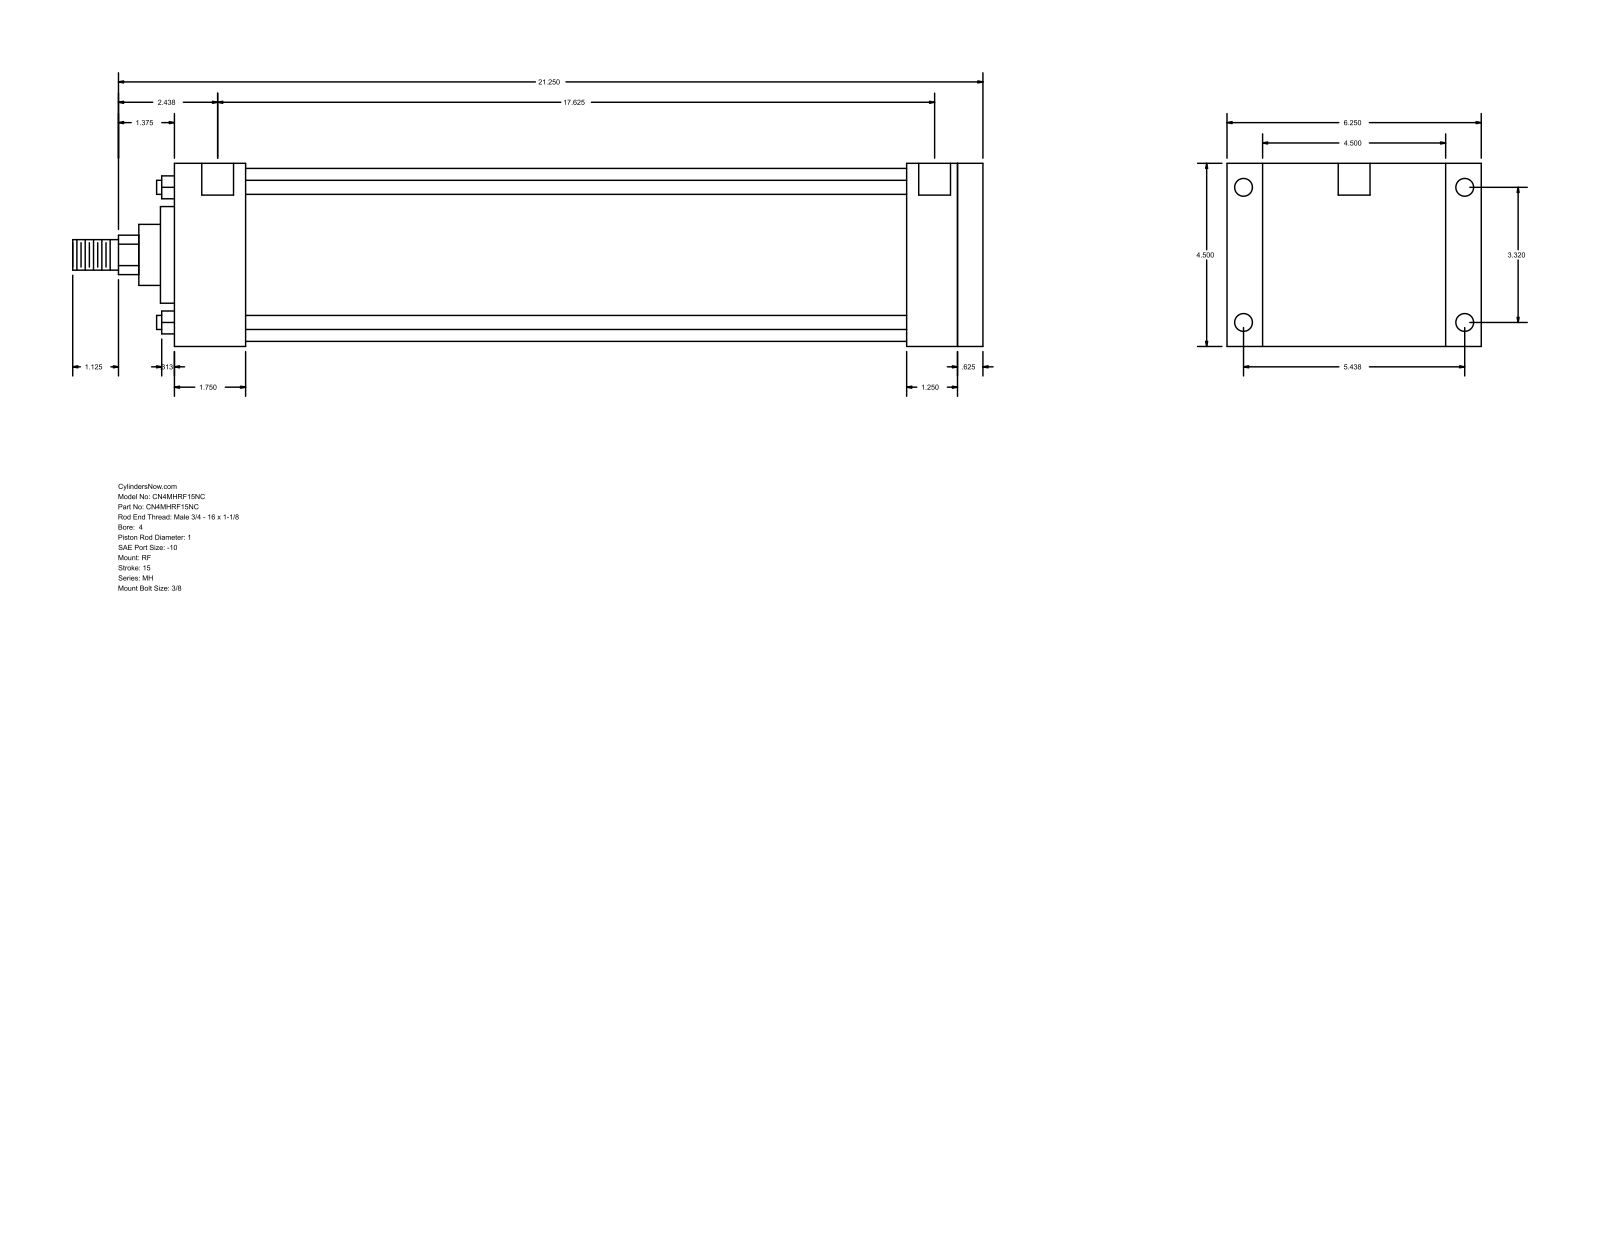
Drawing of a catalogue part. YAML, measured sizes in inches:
part_name: "MH_RF__0400_1"
step_written_by: "GSSL Pune (CONFIG_CONTROL_DESIGN)"
units: inches
bodies: {solids: 0, faces: 94, planar: 65, cylindrical: 29, other: 0}
overall_size: [22.375, 6.25, 4.5]
round_holes:
  - {diameter: 0.344, count: 4}
  - {diameter: 0.438, count: 4}
  - {diameter: 0.781, count: 2}
round_bosses_or_shafts:
  - {diameter: 0.345, count: 4}
  - {diameter: 4.25, count: 1}
  - {diameter: 2.375, count: 1}
  - {diameter: 1.5, count: 1}
  - {diameter: 1, count: 1}
  - {diameter: 0.75, count: 1}
partial_cylinders:
  - {radius: 0.484, count: 1}
face_to_face_distances: [4.5, 19.875, 19.25, 0.625, 1.875, 1.75, 17.5, 18.125, 18, 16.25]
hole_center_spacings: [3.32, 5.438, 6.371, 17.75, 0.062, 0.063, 17.625, 17.687]
